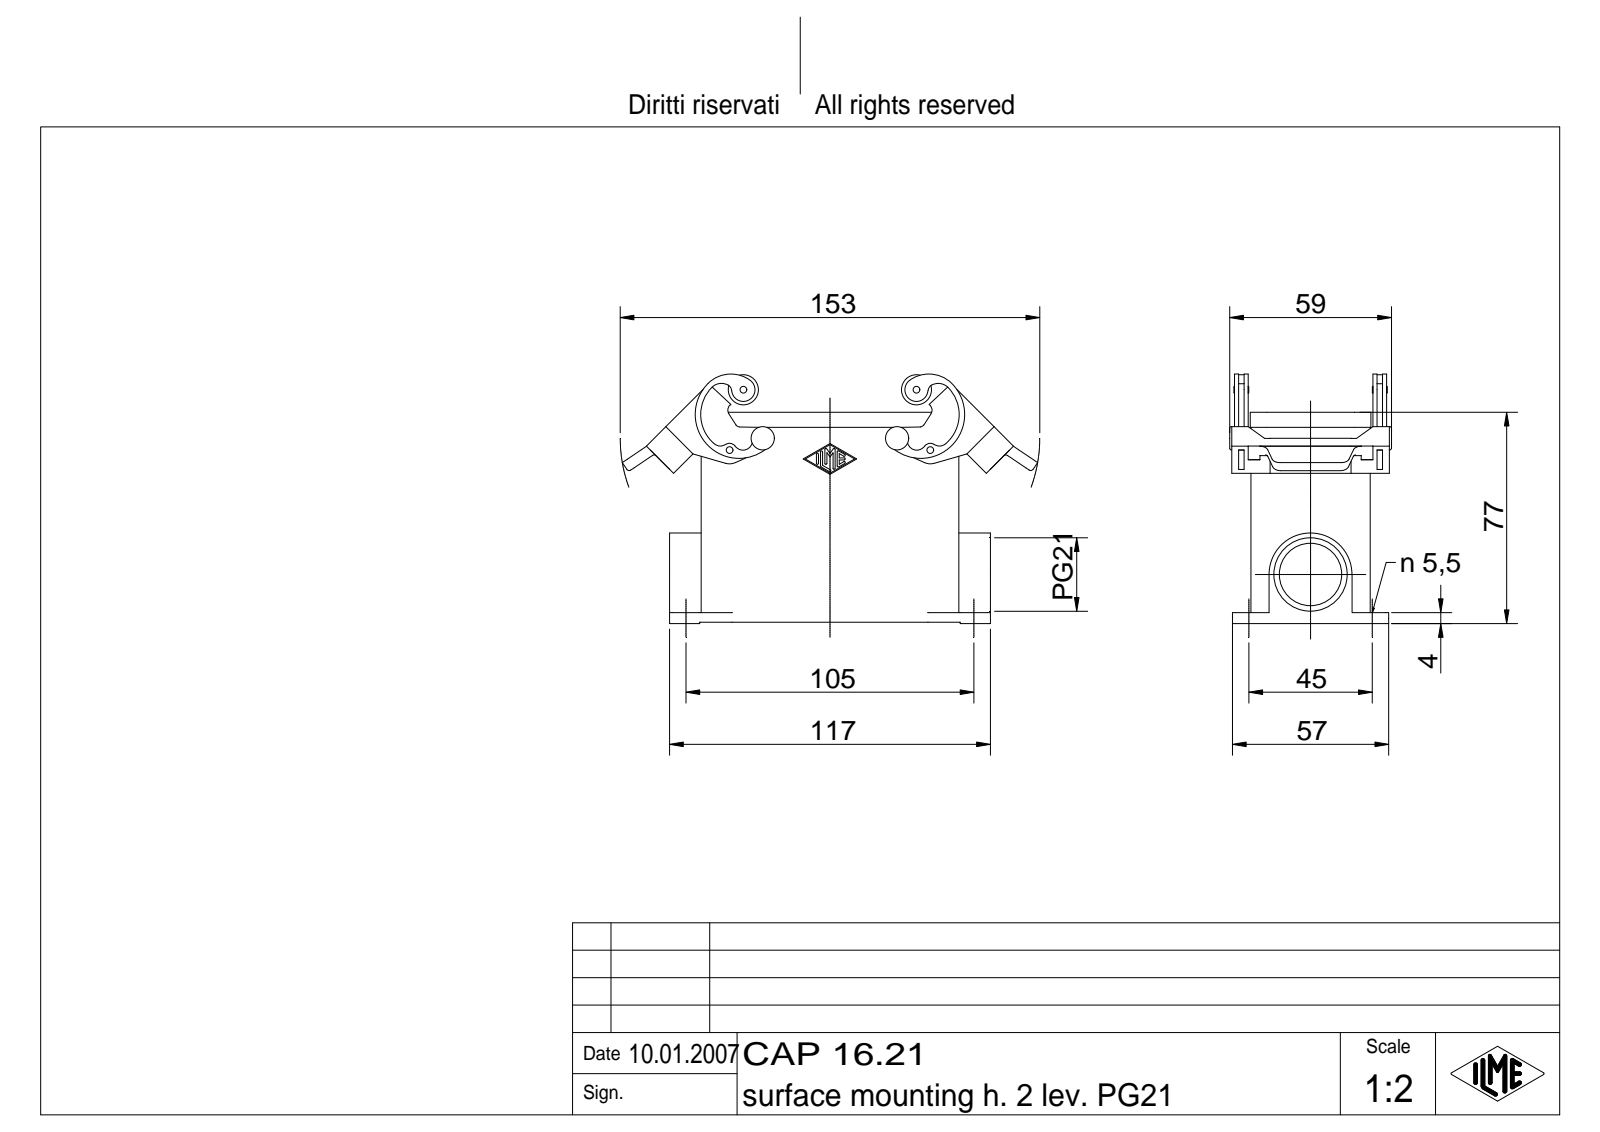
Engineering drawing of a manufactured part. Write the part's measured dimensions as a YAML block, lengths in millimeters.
part_name: "CAP 16.21"
step_written_by: "Autodesk Inventor 7 (AUTOMOTIVE_DESIGN)"
units: millimeters
bodies: {solids: 1, faces: 749, planar: 191, cylindrical: 205, other: 353}
overall_size: [151.49, 90.94, 58]
volume: 125808
surface_area: 68944
round_holes:
  - {diameter: 2, count: 4}
  - {diameter: 5.5, count: 4}
  - {diameter: 2.5, count: 2}
  - {diameter: 22.78, count: 1}
  - {diameter: 26.78, count: 1}
round_bosses_or_shafts:
  - {diameter: 11, count: 2}
  - {diameter: 5, count: 2}
  - {diameter: 3, count: 2}
partial_cylinders:
  - {radius: 1, count: 20}
  - {radius: 0.38, count: 14}
  - {radius: 3, count: 12}
  - {radius: 6, count: 8}
  - {radius: 2.5, count: 6}
  - {radius: 1.5, count: 4}
  - {radius: 2, count: 4}
  - {radius: 3.5, count: 4}
face_to_face_distances: [3, 40.5, 43.5, 37.5, 3.5, 4, 0.75, 50.5, 11, 40.75]
hole_center_spacings: [22.56, 45, 71.62, 105, 114.24, 63.14, 73.18]
